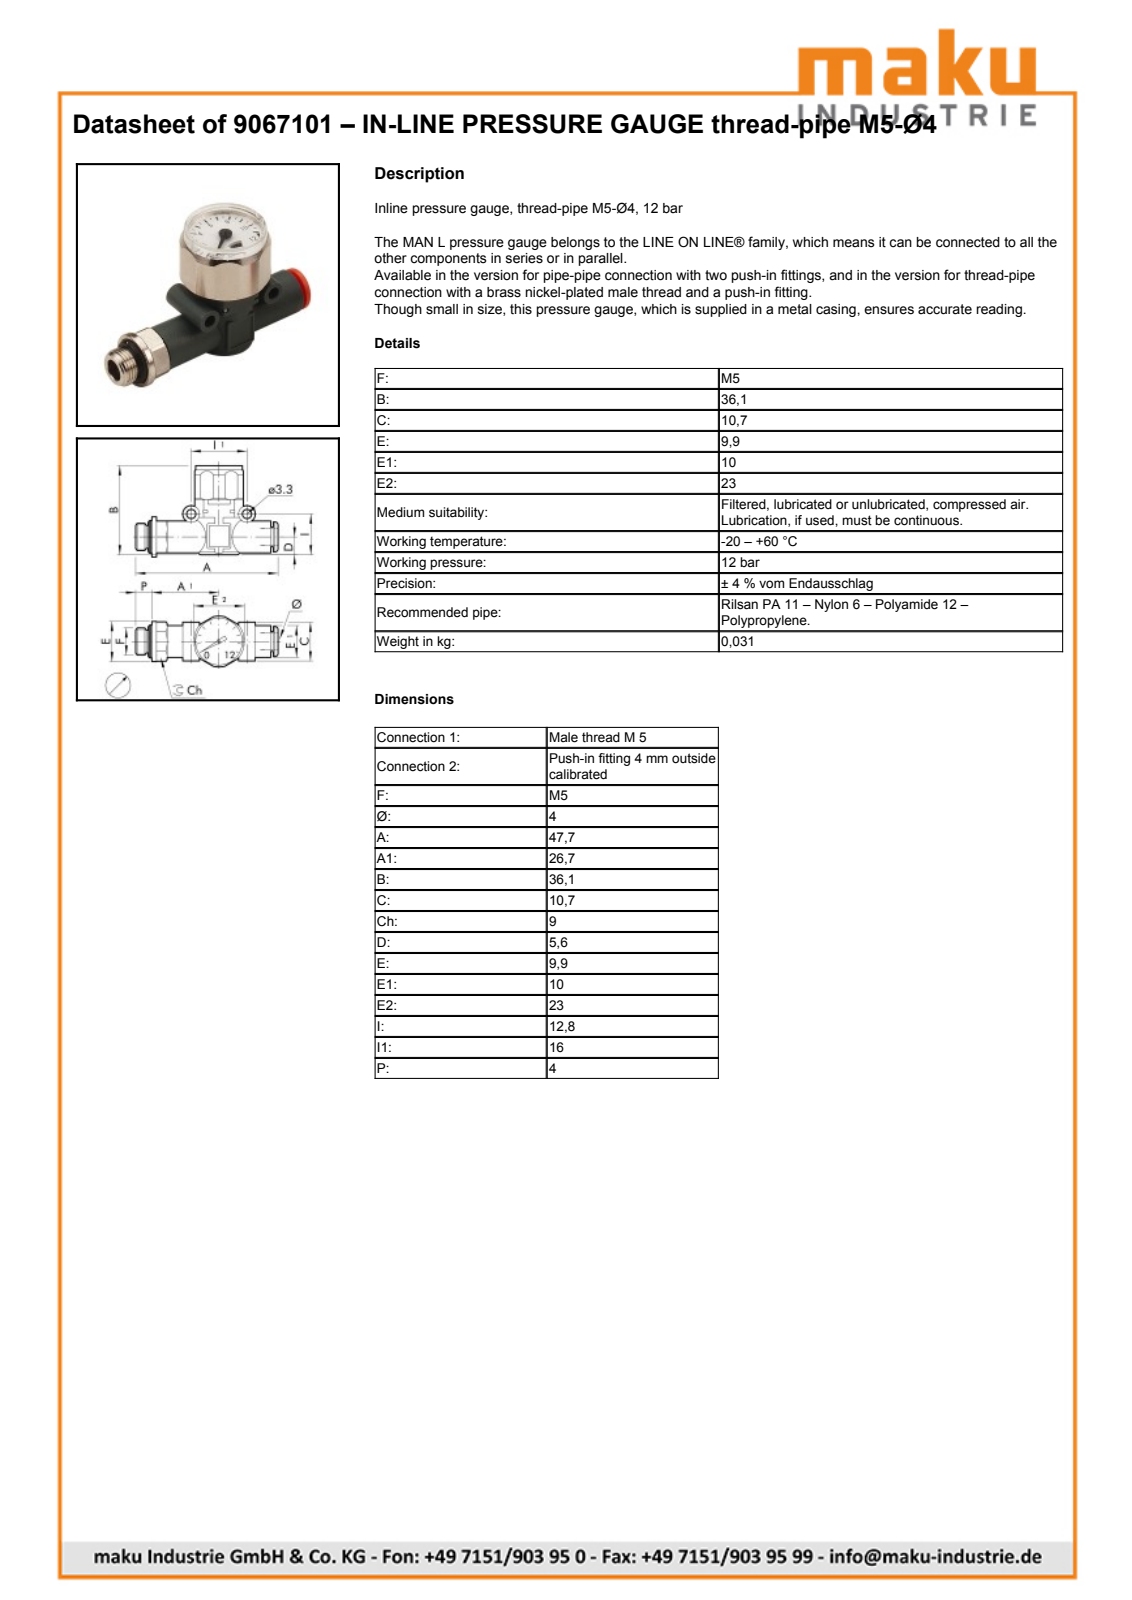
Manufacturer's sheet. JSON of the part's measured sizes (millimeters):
{"part_name": "9067101; LINE-ON-LINE D4 V2v/V3V_L body; LINE-ON-LINE D4 VNR-L bushing; LINE-ON-LINE D4-M5 MAN-L thread port (+1 more)", "step_written_by": "PARTsolutions (AUTOMOTIVE_DESIGN)", "units": "millimeters", "bodies": {"solids": 4, "faces": 227, "planar": 153, "cylindrical": 62, "other": 12}, "overall_size": [47.6, 36.1, 22.73], "volume_mm3": 9046, "surface_area_mm2": 6067, "round_holes": [[3.3, 2], [2.5, 1], [3.6, 1], [4, 1], [4.1, 1], [6, 1], [6.5, 1], [7.5, 1], [7.8, 1], [8.1, 1], [17.61, 1], [18.86, 1]], "round_bosses_or_shafts": [[6, 3], [20.96, 1], [17.91, 1], [11, 1], [9.9, 1], [9.2, 1], [9, 1], [6.2, 1]], "partial_cylinders_radius": [[0.71, 1], [3.75, 1], [5.65, 1], [5.7, 1], [6.9, 1], [11.5, 1]], "face_to_face_distances": [14.41, 22, 6, 16, 16.25, 5.75, 5.21, 19.62, 4.75, 10.2], "hole_center_spacings": [10.76, 16]}
